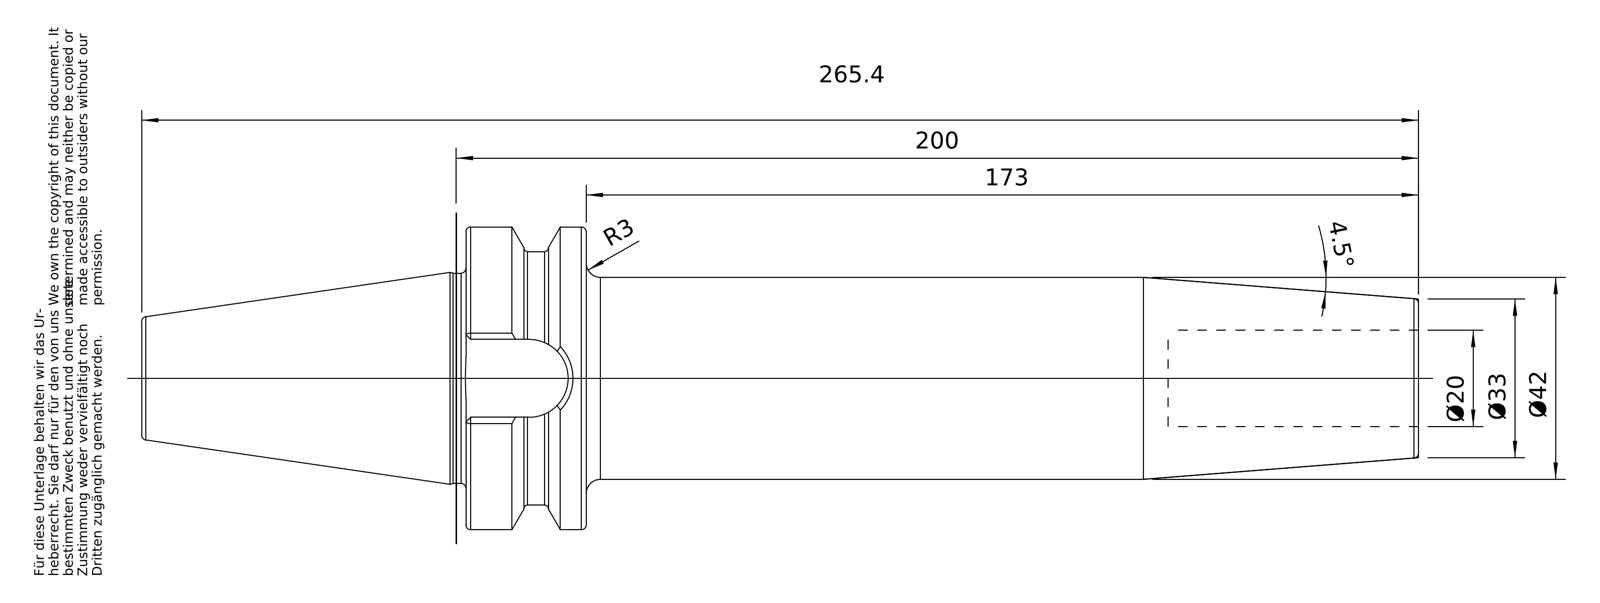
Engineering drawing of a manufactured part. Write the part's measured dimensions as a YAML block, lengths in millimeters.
part_name: "40-646-20"
step_written_by: "PRO/ENGINEER BY PARAMETRIC TECHNOLOGY CORPORATION, 2010430 (CONFIG_CONTROL_DESIGN)"
units: millimeters
bodies: {solids: 1, faces: 96, planar: 26, cylindrical: 22, other: 48}
overall_size: [265.4, 62.98, 62.98]
volume: 333969
surface_area: 46407
round_holes:
  - {diameter: 13.84, count: 1}
  - {diameter: 17.01, count: 1}
  - {diameter: 17.5, count: 1}
  - {diameter: 20, count: 1}
round_bosses_or_shafts:
  - {diameter: 62.98, count: 1}
  - {diameter: 52.75, count: 1}
  - {diameter: 43.75, count: 1}
  - {diameter: 42, count: 1}
  - {diameter: 16.01, count: 1}
partial_cylinders:
  - {radius: 8.1, count: 1}
face_to_face_distances: [25, 198, 173, 44.9, 146, 121, 52, 16.2, 67.4, 92.4]
